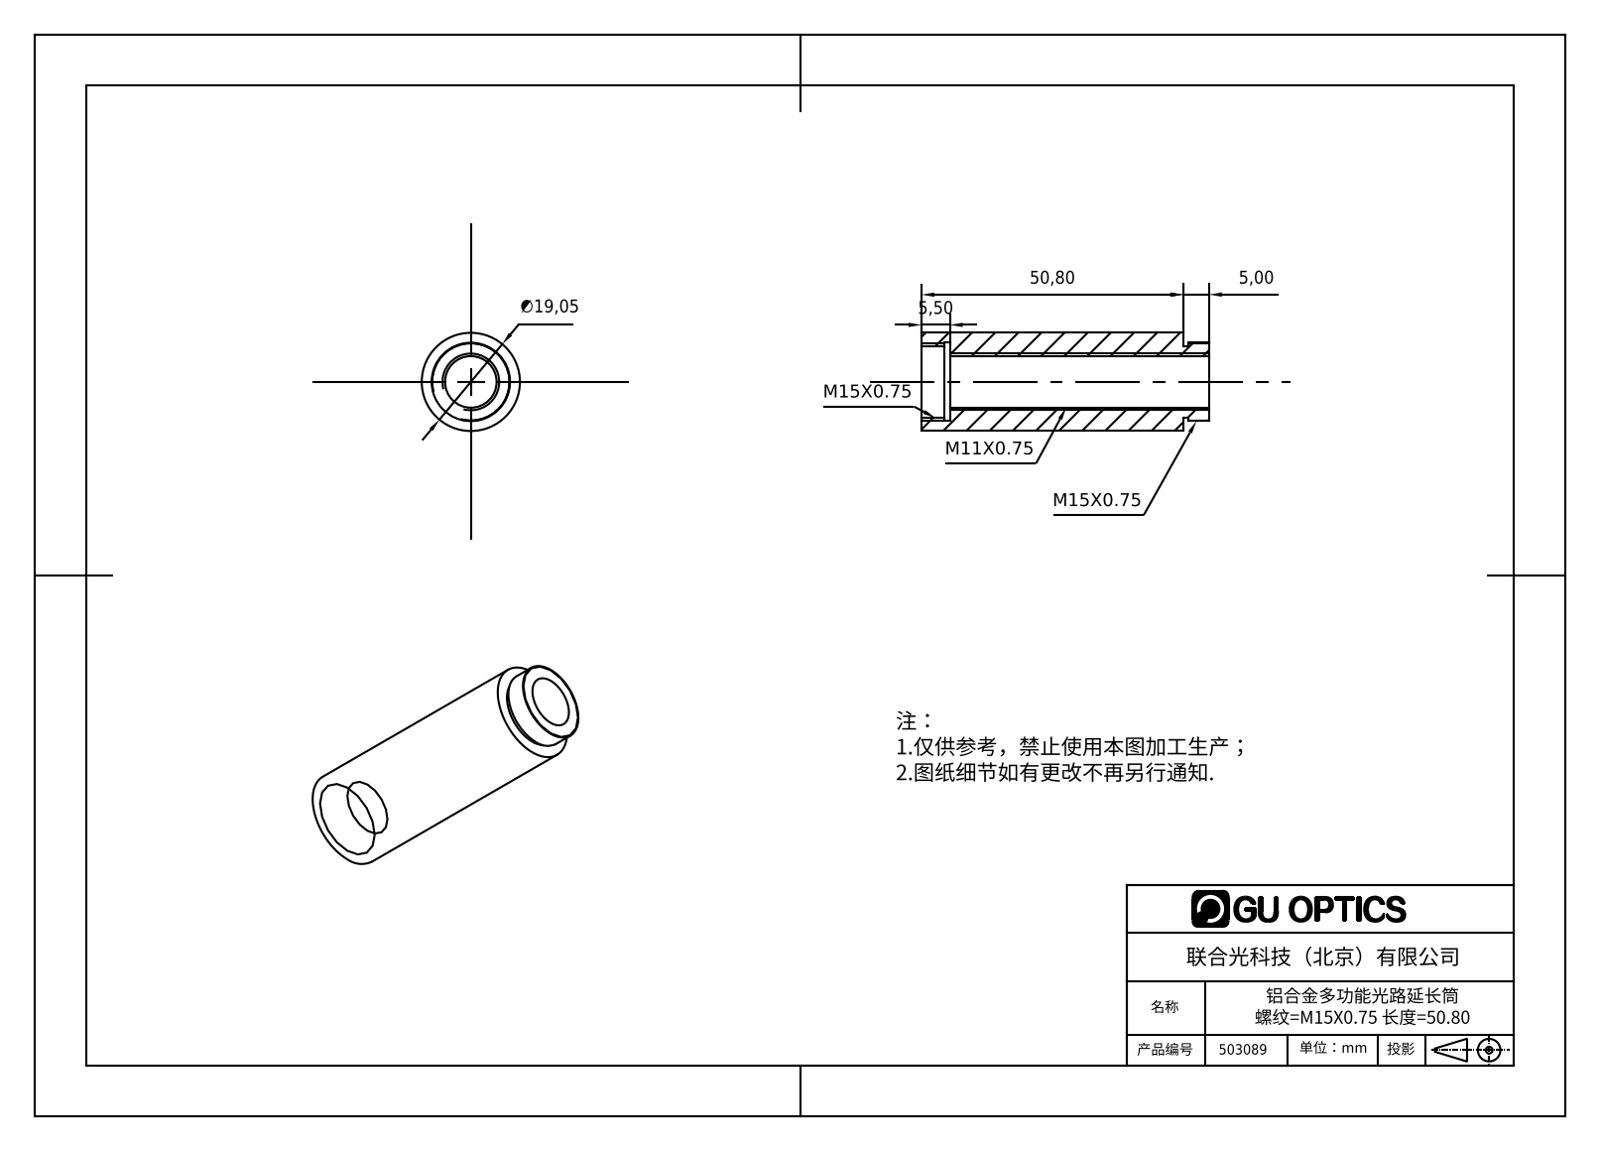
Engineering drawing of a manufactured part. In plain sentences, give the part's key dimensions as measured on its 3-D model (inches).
The part is named "503089". Its 3-D file was written by "SolidWorks 2016 (AUTOMOTIVE_DESIGN)". It is 1 solid with 18 faces: 6 planar, 12 cylindrical and 0 other. Overall it measures 2.197 by 0.75 by 0.75 inches. Its volume is 0.643 cubic inches and its surface area 8.717 square inches. Round holes: 1 of diameter 0.394, 1 of diameter 0.551, 1 of diameter 0.598. Round bosses or shafts: 1 of diameter 0.75. The main face-to-face distances are 2, 0.217, 1.783, 2.197, 1.98, 0.197, 0.039, 1.823, 2.039, 0.157.
